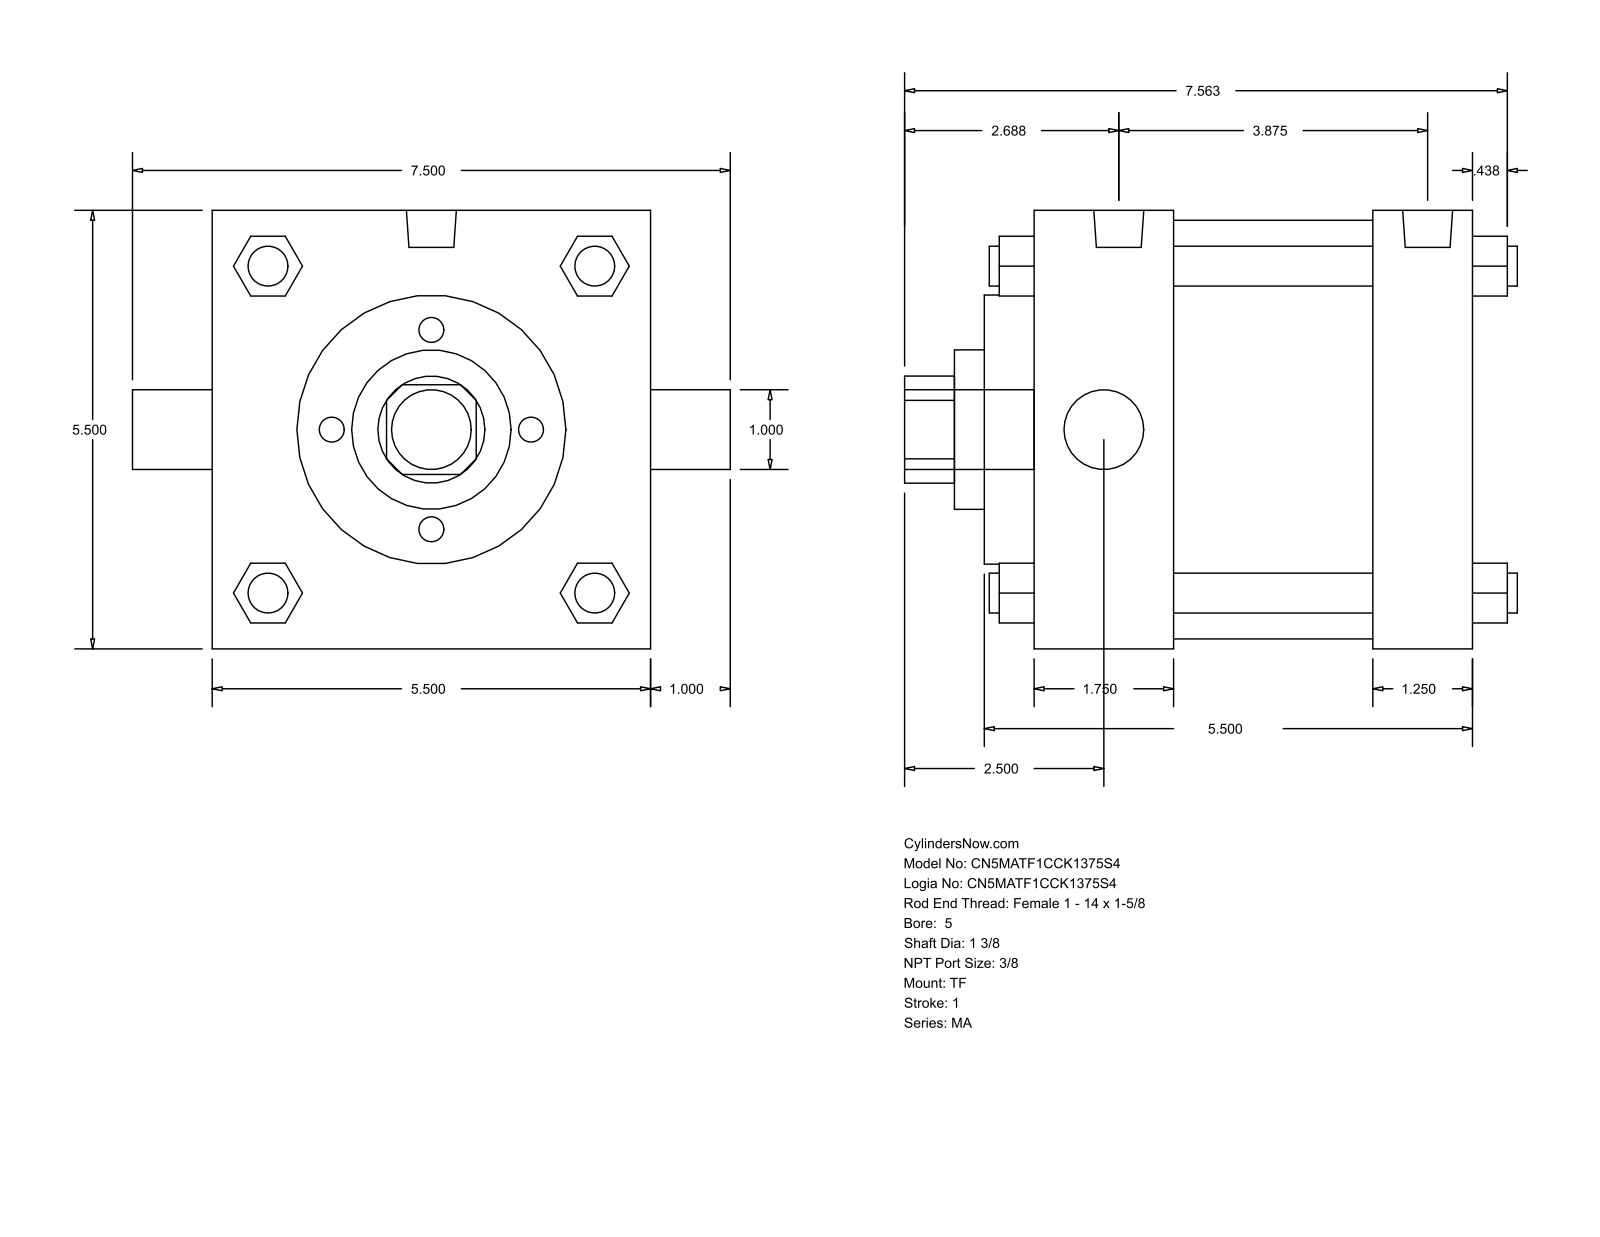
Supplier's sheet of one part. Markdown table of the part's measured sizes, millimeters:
| quantity | value |
| --- | --- |
| part name | MA_TF__0500_1.375 |
| STEP written by | GSSL Pune (CONFIG_CONTROL_DESIGN) |
| units | millimeters |
| bodies | 0 solids, 122 faces (93 planar, 29 cylindrical, 0 other) |
| overall size | 195.26 × 190.5 × 139.7 |
| round holes (diameter × count) | 25.4 × 1, 34.92 × 1, 50.8 × 1, 85.72 × 1, 133.35 × 1 |
| round bosses / shafts (diameter × count) | 12.7 × 4, 11.11 × 3, 15.93 × 2, 25.4 × 1 |
| partial cylindrical surfaces (radius × count) | 17.06 × 1 |
| main face-to-face distances | 139.7, 107.95, 31.75, 44.45, 63.5, 95.25, 15.87, 60.32, 123.82, 155.57 |
